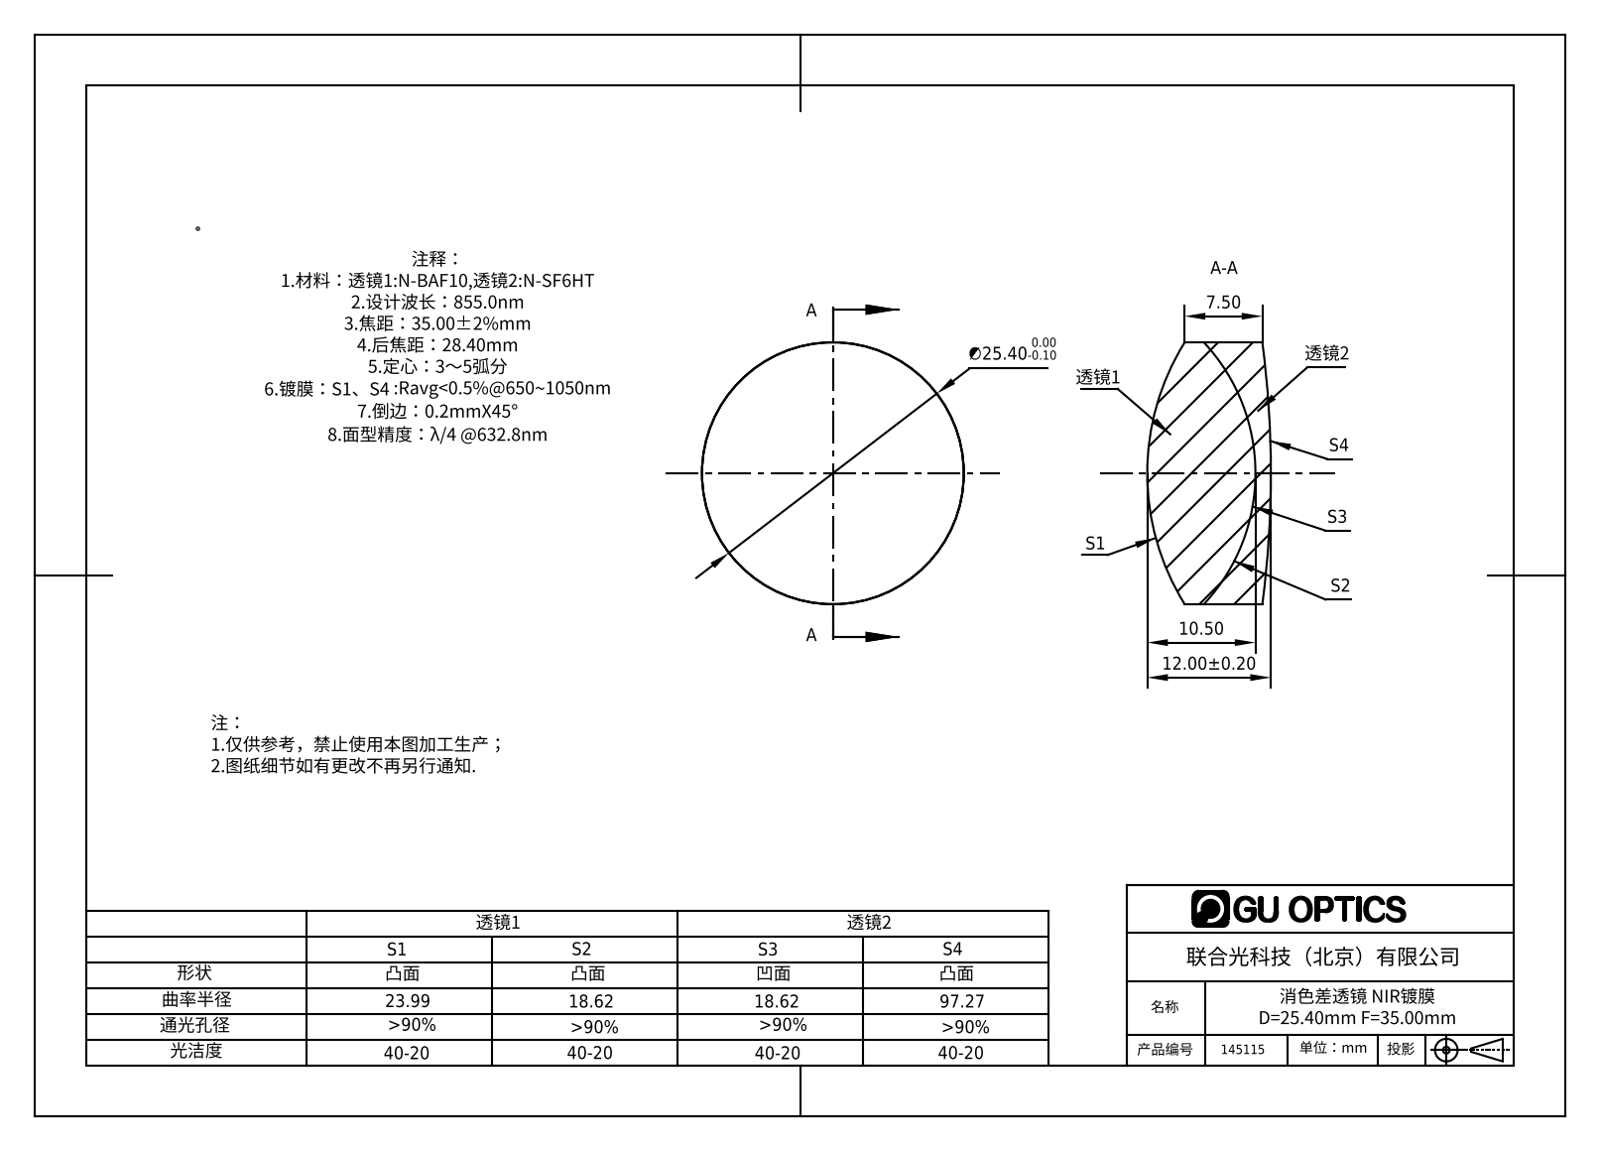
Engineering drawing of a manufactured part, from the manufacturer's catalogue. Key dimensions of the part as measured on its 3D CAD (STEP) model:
Part name (STEP PRODUCT): 145115
STEP written by: SolidWorks 2016 (AUTOMOTIVE_DESIGN)
Units: millimetres
Bodies: 2 solids, 12 faces (0 planar, 4 cylindrical, 8 other)
Overall size (bounding box): 25.4 × 25.4 × 12
Volume: 4 973 mm³ · Surface area: 2 829 mm²
Round bosses / shafts (diameter × count): ⌀25.4 ×1
